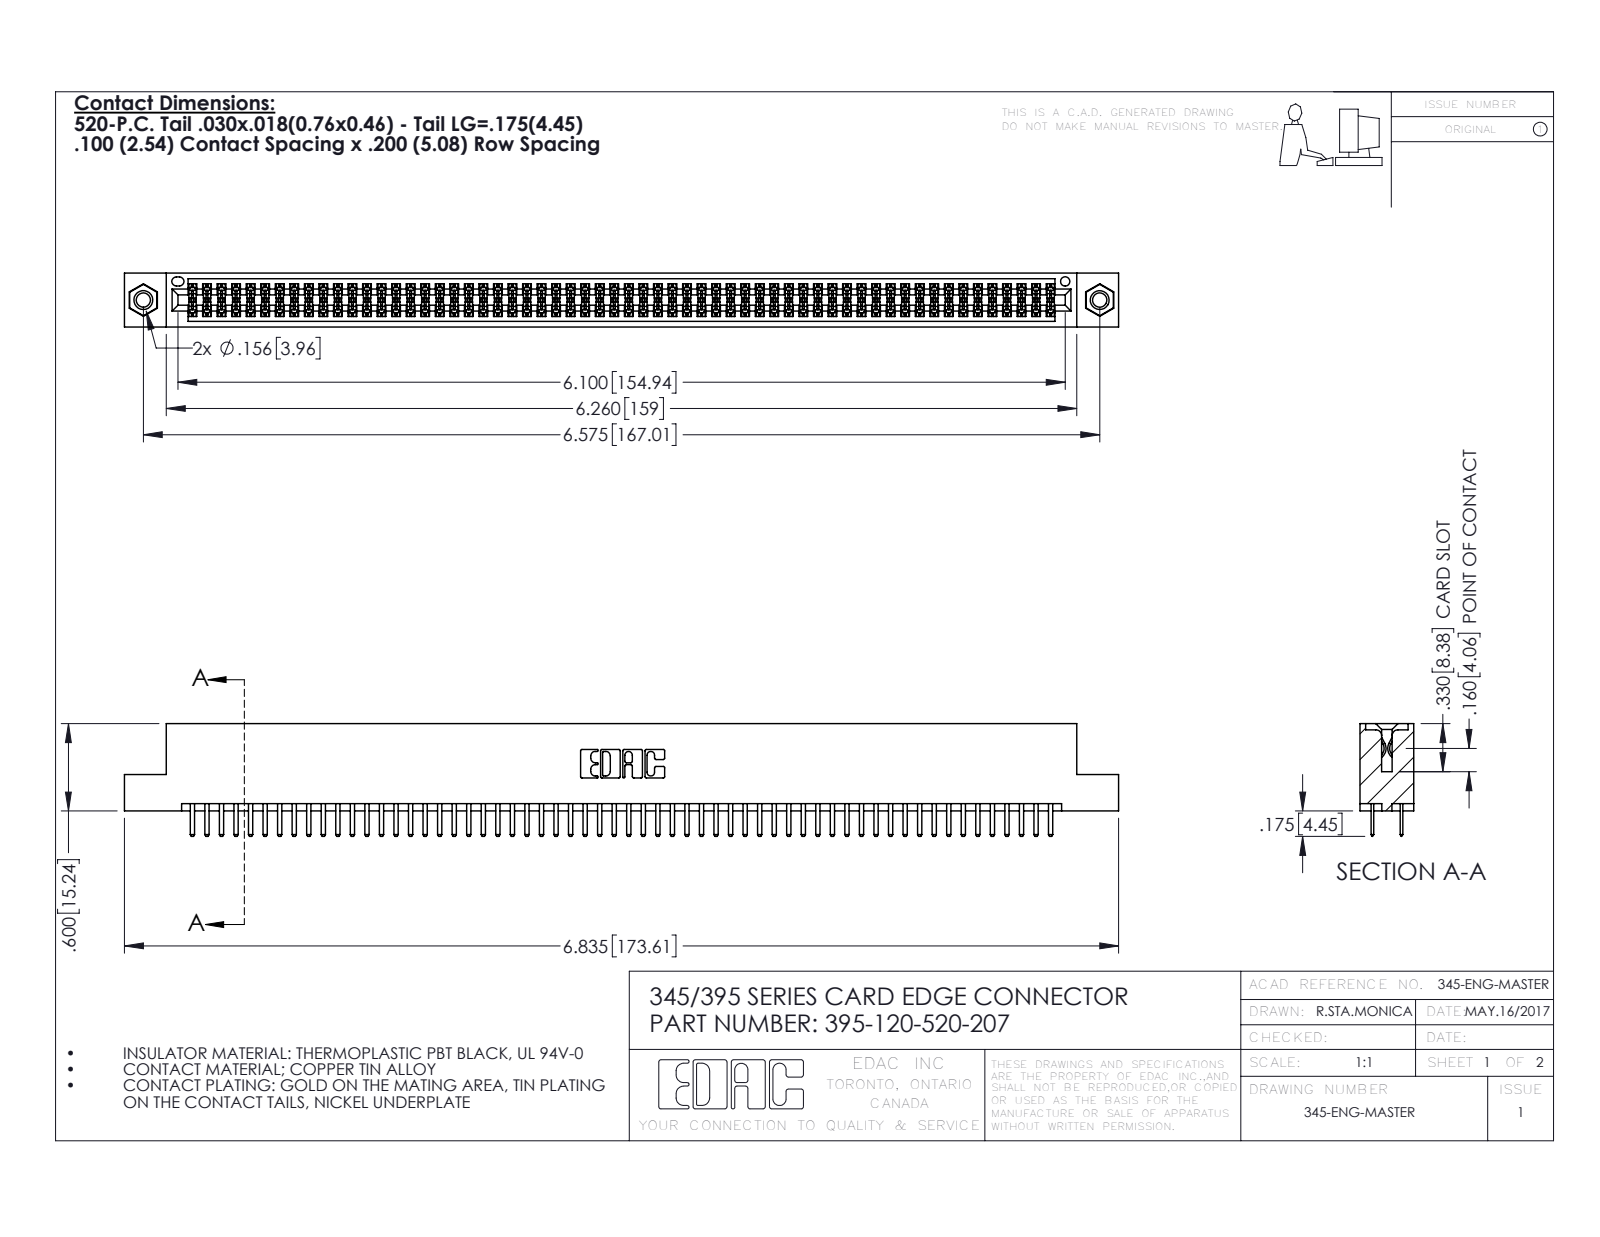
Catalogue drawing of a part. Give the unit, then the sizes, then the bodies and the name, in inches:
Units: inches
Overall size (bounding box): 6.835 × 0.775 × 0.37
Round holes (diameter × count): ⌀0.098 ×2, ⌀0.125 ×2, ⌀0.156 ×2, ⌀0.064 ×1
Round bosses / shafts (diameter × count): ⌀0.155 ×2
Partial cylindrical surfaces — rounded edges, fillets, slot ends (radius × count): R0.006 ×180, R0.01 ×124, R0.01 ×22, R0.007 ×6, R0.031 ×6, R0.026 ×3, R0.014 ×2, R0.019 ×2
Main face-to-face distances: 0.072, 0.298, 0.2, 0.37, 0.098, 0.272, 0.025, 0.225, 0.022, 0.072
Hole centre spacings: 0.27, 6.339, 6.575
Volume: 1.035 in³ · Surface area: 39.28 in²
Bodies: 123 solids, 6666 faces (4312 planar, 2338 cylindrical, 16 other)
Part name (STEP PRODUCT): 395-120-520-207; 345 Part_Flush Mounting Lugs - 0.156 Dia-TI; 345-250-001_345-250-005-103; 345-292-001_345-293-120
STEP written by: SolidWorks 2016 (CONFIG_CONTROL_DESIGN)
